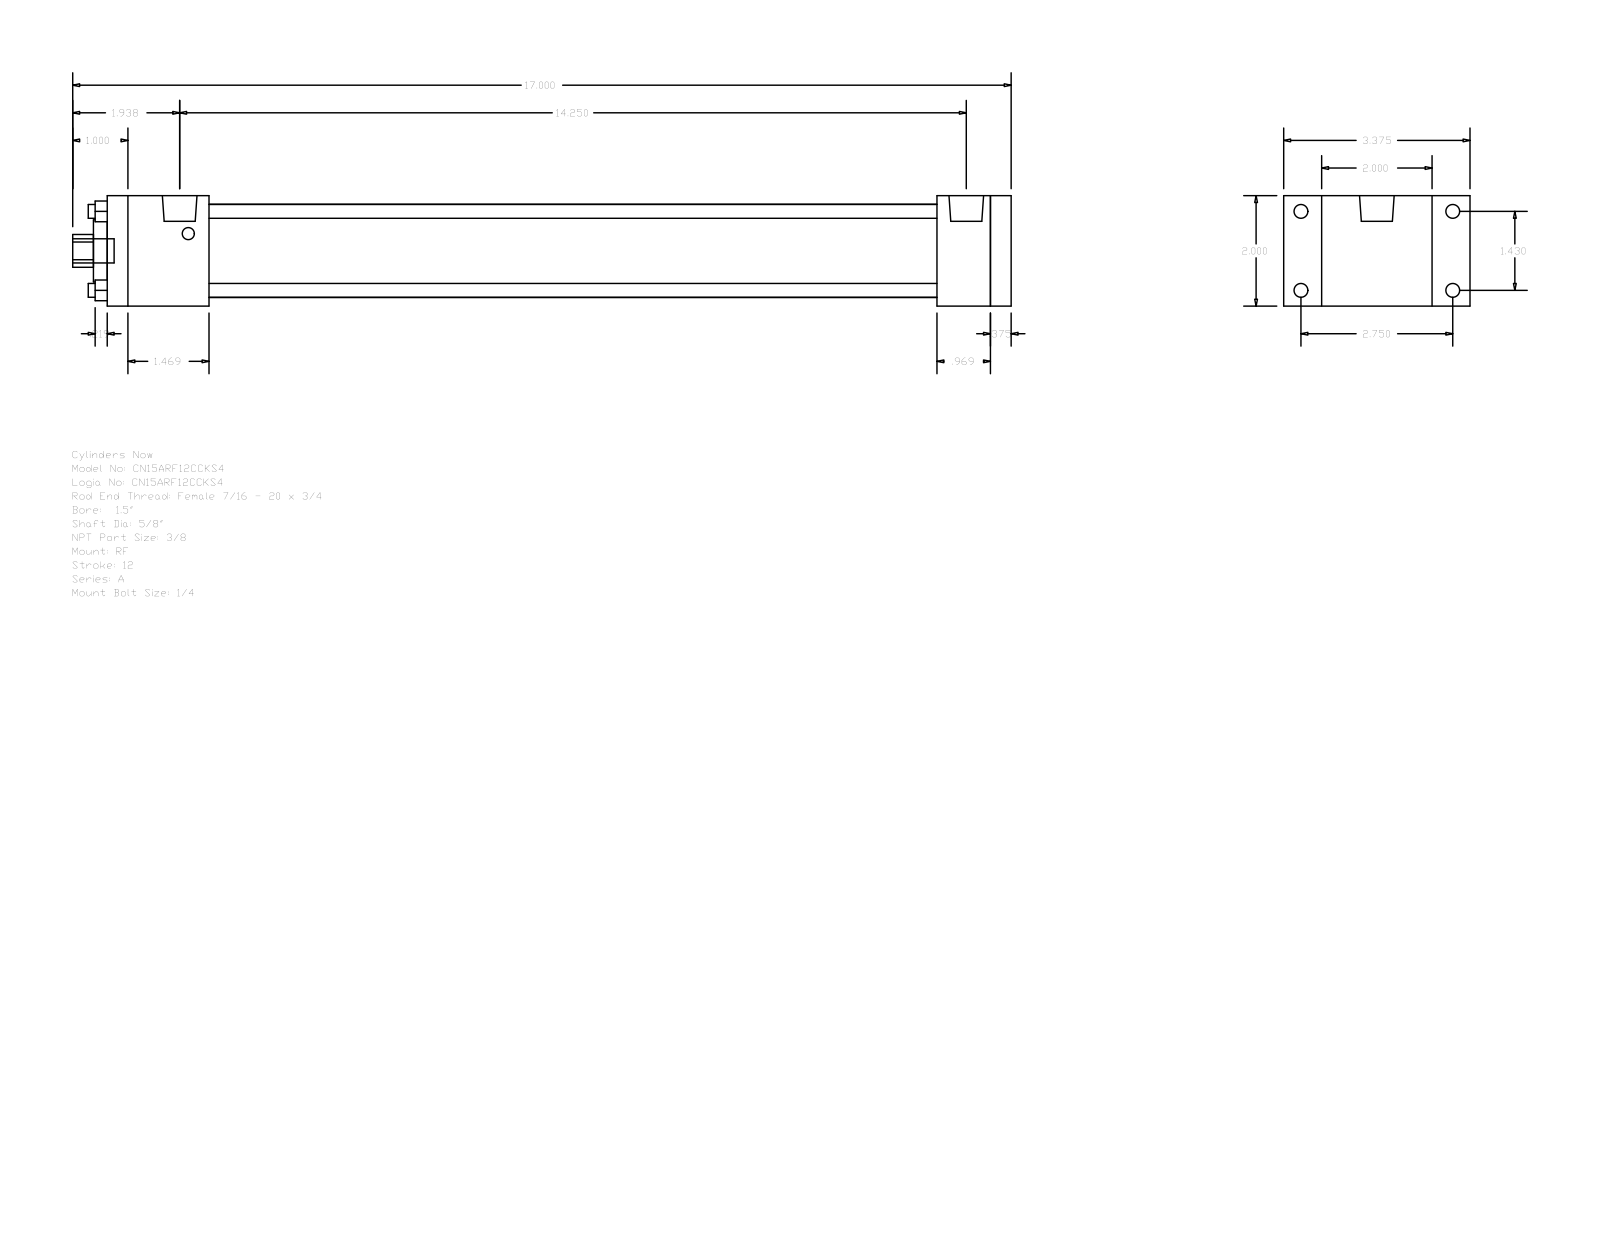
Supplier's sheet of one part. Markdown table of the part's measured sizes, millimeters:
| quantity | value |
| --- | --- |
| part name | A_RF__0150_0.625 |
| STEP written by | GSSL Pune (CONFIG_CONTROL_DESIGN) |
| units | millimeters |
| bodies | 0 solids, 92 faces (64 planar, 28 cylindrical, 0 other) |
| overall size | 431.8 × 85.72 × 50.8 |
| round holes (diameter × count) | 6.35 × 4, 15.88 × 1, 28.57 × 1, 42.93 × 1 |
| round bosses / shafts (diameter × count) | 6.35 × 4, 5.56 × 4, 15.93 × 2, 11.11 × 1 |
| partial cylindrical surfaces (radius × count) | 7.54 × 1 |
| main face-to-face distances | 50.8, 9.53, 415.92, 406.39, 381.79, 24.6, 34.13, 46.83, 334.96, 359.56 |
| hole center spacings | 25.68, 36.32, 51.36 |
